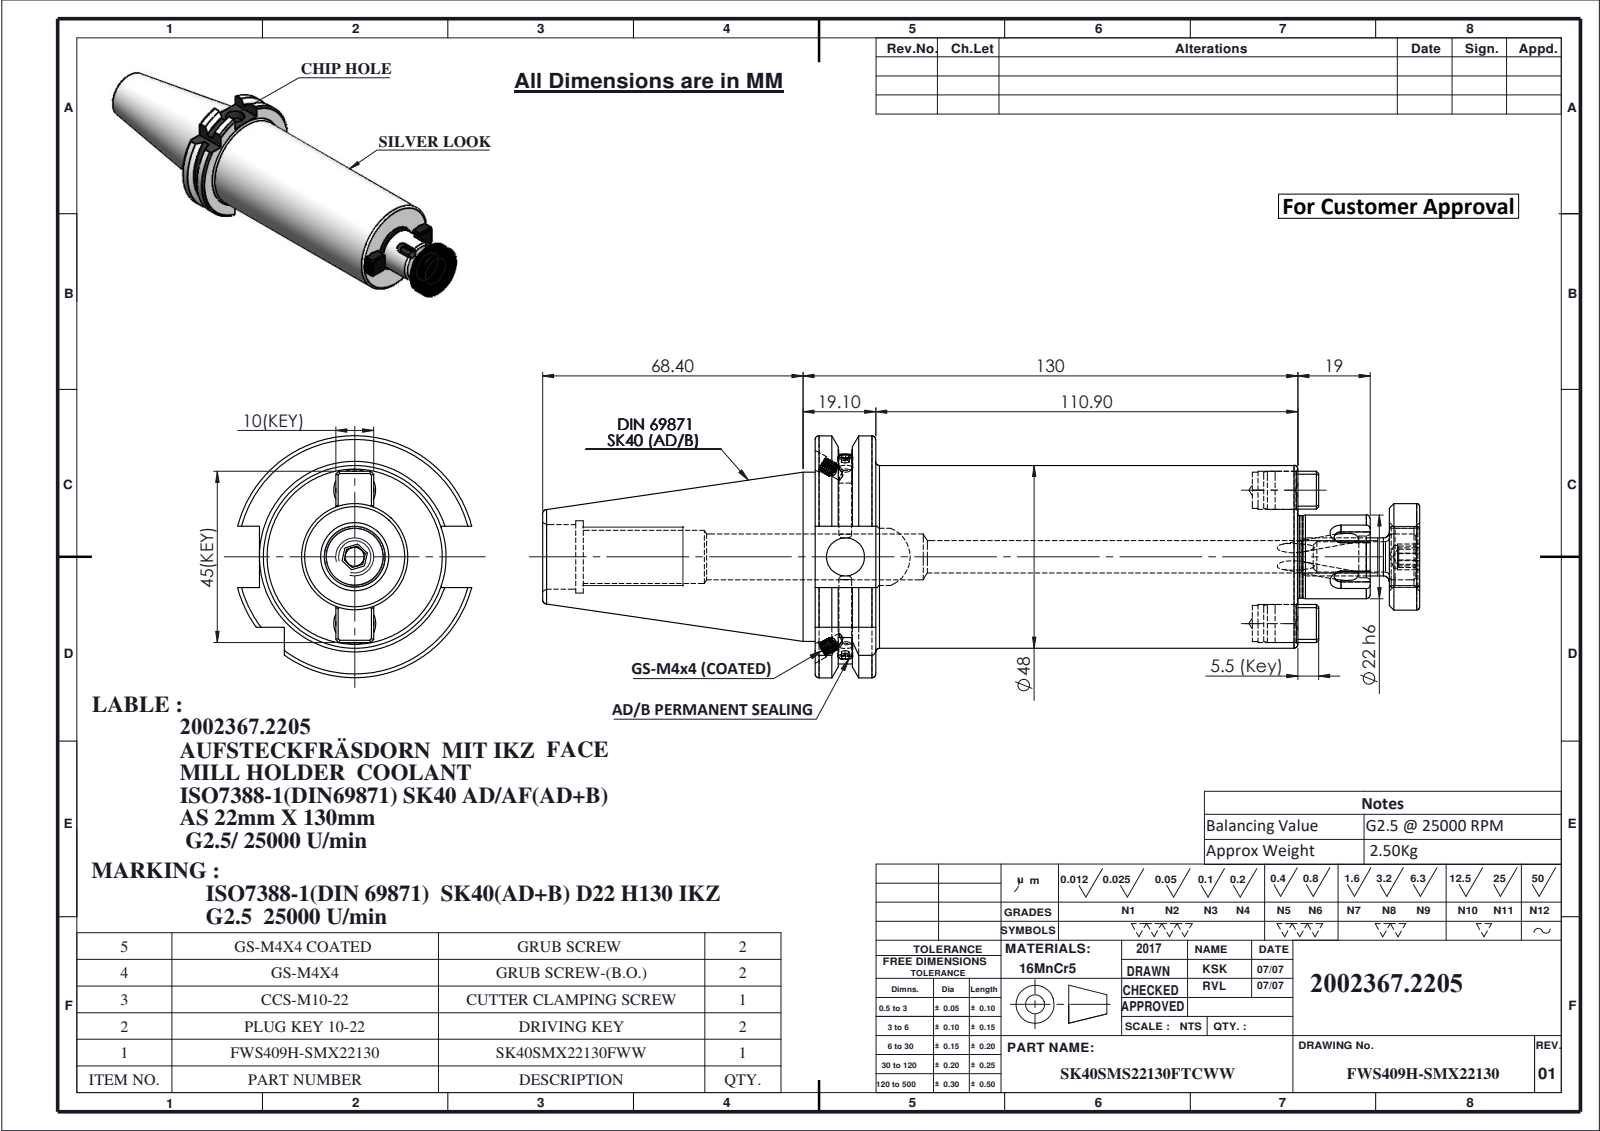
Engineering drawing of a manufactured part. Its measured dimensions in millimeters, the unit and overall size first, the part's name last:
Units: millimetres
Overall size (bounding box): 230.4 × 63.55 × 61.48
Round holes (diameter × count): ⌀3 ×4, ⌀3.3 ×3, ⌀10 ×3, ⌀4.5 ×2, ⌀9.5 ×2, ⌀6 ×1, ⌀8.5 ×1, ⌀11 ×1, ⌀12 ×1, ⌀14 ×1, ⌀15 ×1, ⌀17 ×1
Round bosses / shafts (diameter × count): ⌀4 ×4, ⌀10.02 ×2, ⌀9.98 ×2, ⌀2.9 ×2, ⌀48 ×1, ⌀44.45 ×1, ⌀28 ×1, ⌀22 ×1
Partial cylindrical surfaces — rounded edges, fillets, slot ends (radius × count): R2 ×4, R6.5 ×2, R8.05 ×1, R28.12 ×1, R31.77 ×1
Main face-to-face distances: 126.8, 15.9, 110.9, 158.8, 142.9, 32, 8, 150.8, 134.9, 24
Hole centre spacings: 17.5, 35
Volume: 307 783 mm³ · Surface area: 49 945 mm²
Bodies: 10 solids, 465 faces (148 planar, 130 cylindrical, 187 other)
Part name (STEP PRODUCT): GS-M4X4-COATING_DIN 913 - M4 x 4-N; CCS-M10-22 LONG; SK40SMX22130FWW; M4X4_DIN 913 - M4 x 4-N (+6 more)
STEP written by: SolidWorks 2024 (CONFIG_CONTROL_DESIGN)
